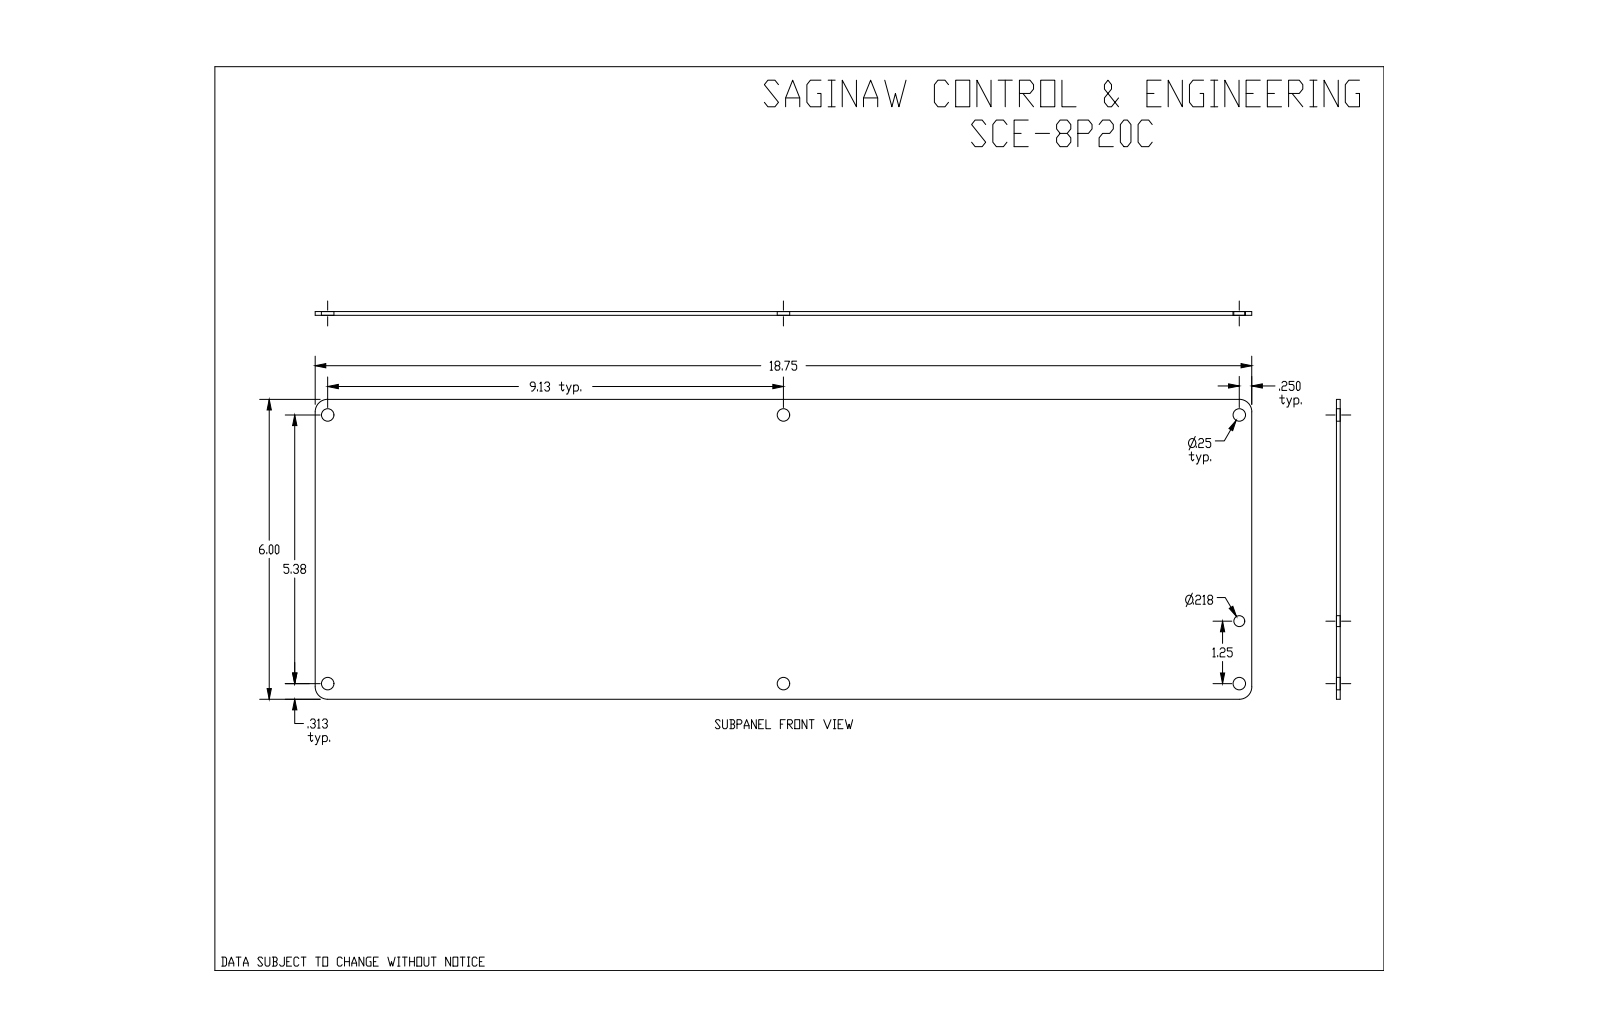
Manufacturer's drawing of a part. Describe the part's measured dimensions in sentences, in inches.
The part is named "SCE-8P20C". Its 3-D file was written by "SolidWorks 2019 (CONFIG_CONTROL_DESIGN)". It is 1 solid with 17 faces: 6 planar, 11 cylindrical and 0 other. Overall it measures 18.75 by 6 by 0.075 inches. Its volume is 8.409 cubic inches and its surface area 228.3 square inches. Round holes: 6 of diameter 0.25, 1 of diameter 0.218. Partial cylindrical surfaces (rounded edges, fillets, slot ends): 4 of radius 0.25. The main face-to-face distances are 0.075, 6, 18.75. The hole center spacings are 9.125, 10.59, 5.375, 18.25, 19.025, 1.25, 4.125, 9.21.
